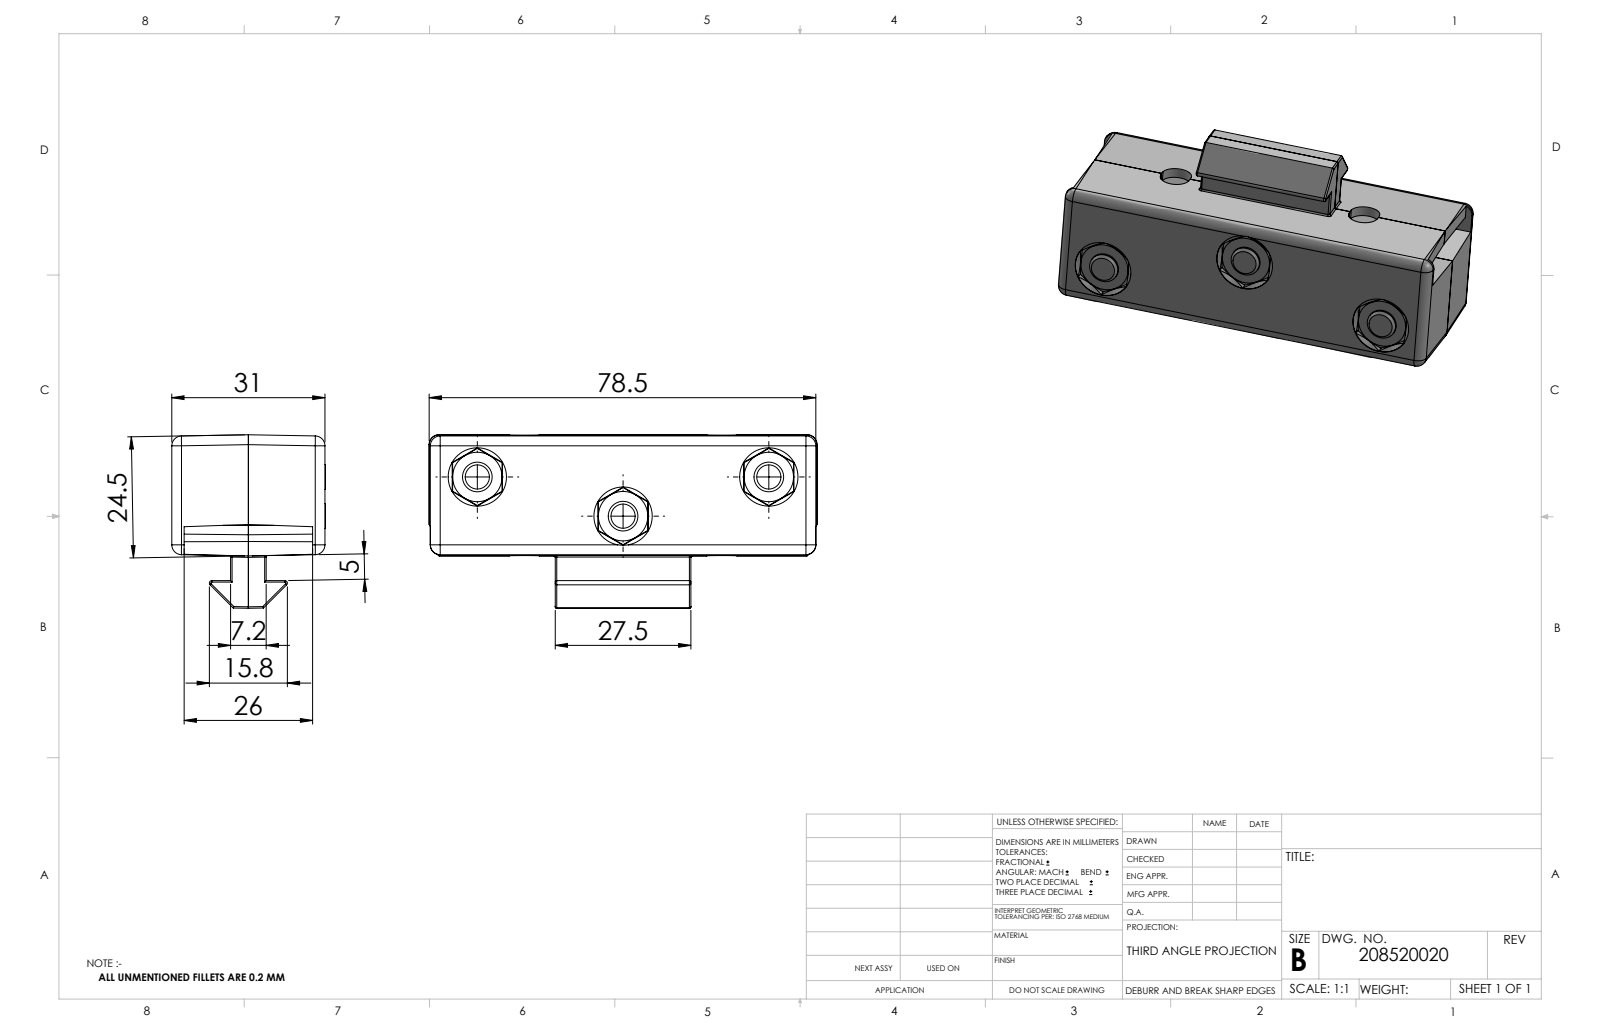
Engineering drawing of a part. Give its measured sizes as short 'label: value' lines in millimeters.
name: 208520020_C_1
written by: SolidWorks 2014 (CONFIG_CONTROL_DESIGN)
unit: mm
bodies: 10 solids, 1283 faces (405 planar, 182 cylindrical, 696 other)
size: 78.5 × 35.1 × 31.1
volume: 39 146 mm³; area: 35 201 mm²
holes: 5× ⌀6, 3× ⌀5, 3× ⌀11.8, 2× ⌀3.1, 2× ⌀8
bosses: 3× ⌀10, 2× ⌀7.8, 2× ⌀3
rounds: 38× R0.5, 32× R0.3, 16× R2, 4× R3
face distances: 2.5, 15.5, 2, 13, 22.5, 24.5, 28.5, 31, 26, 9.4
hole spacings: 18.14, 30.2, 30.54, 45.74, 20, 40, 59
